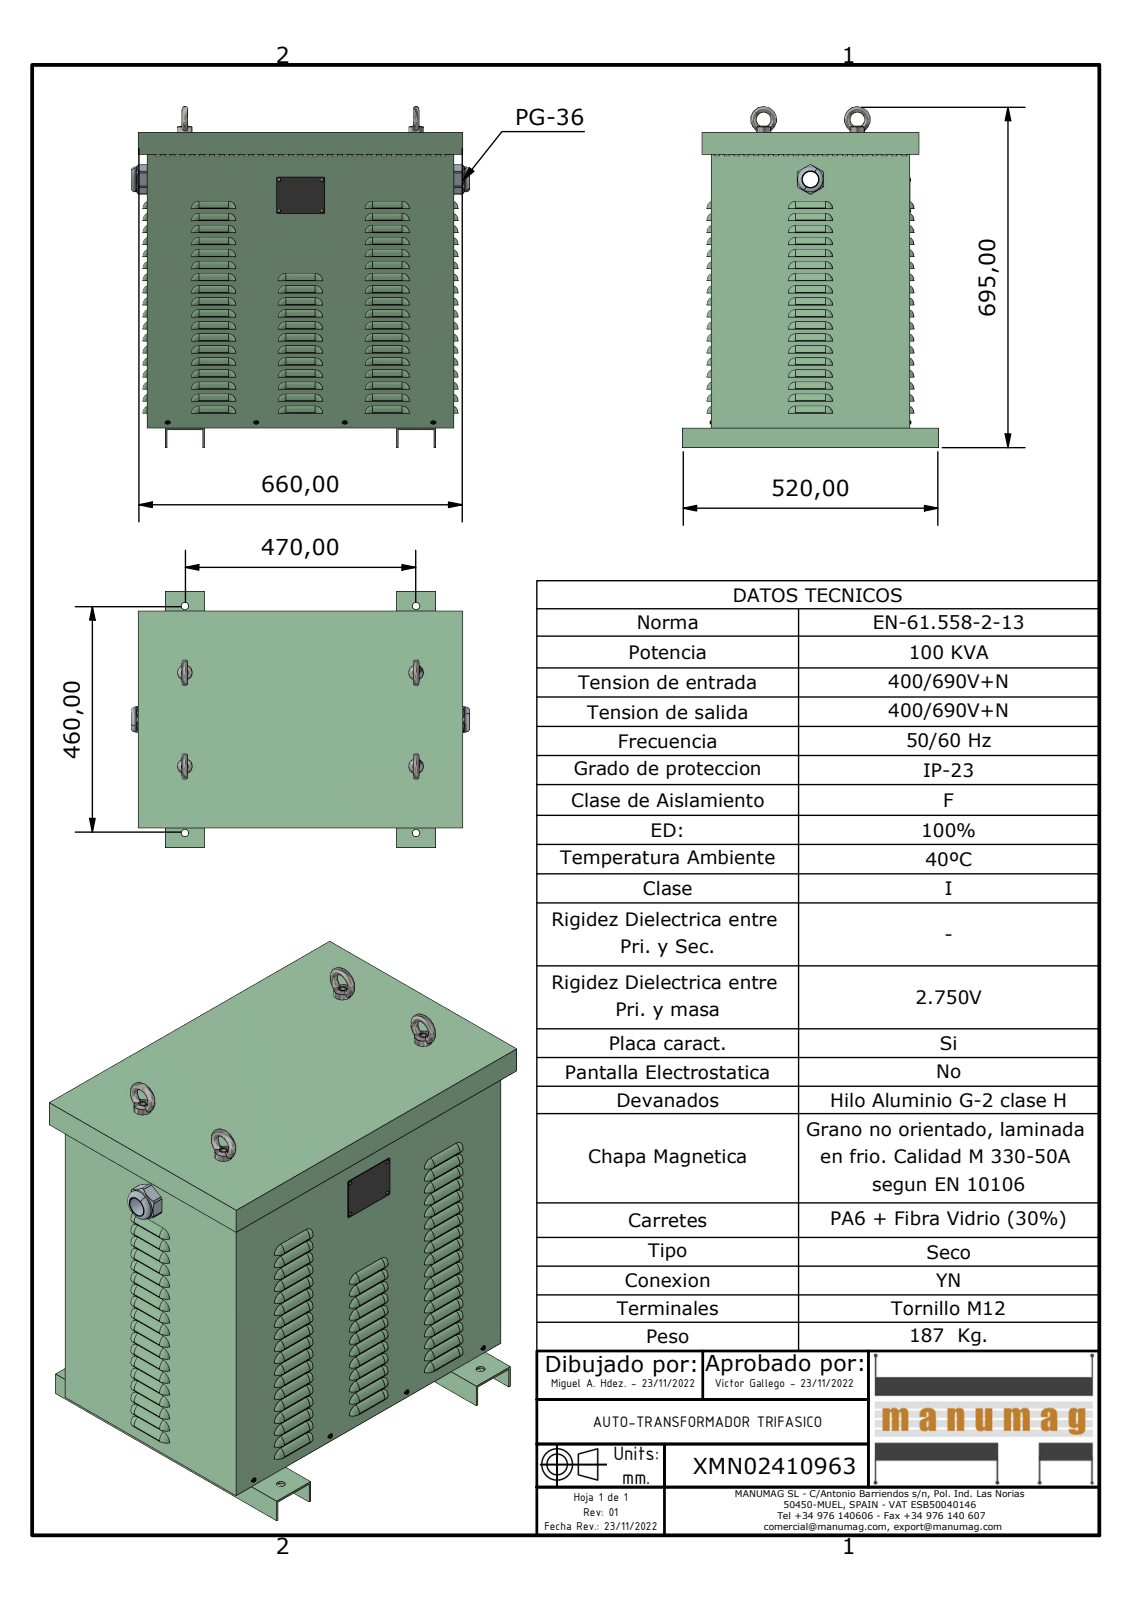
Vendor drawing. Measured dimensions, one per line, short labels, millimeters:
name: XMN02410963; JE100 CUERPO; JE100 BASE; PLACA CARACTERISTICAS (+6 more)
written by: Autodesk Inventor 2023 (AUTOMOTIVE_DESIGN)
unit: mm
bodies: 24 solids, 3065 faces (1141 planar, 1208 cylindrical, 716 other)
size: 695 × 688.2 × 520
volume: 4 880 000 mm³; area: 4 293 000 mm²
holes: 558× ⌀11, 8× ⌀15, 4× ⌀4, 4× ⌀5, 4× ⌀10.11, 1× ⌀32, 1× ⌀48
bosses: 4× ⌀30, 4× ⌀4, 4× ⌀3.62, 4× ⌀3.2, 2× ⌀51.1, 1× ⌀47.45, 1× ⌀47
rounds: 132× R14, 72× R7, 72× R15, 12× R3.88, 8× R2.5, 4× R2, 2× R30
face distances: 2, 400, 600, 621, 398, 402, 602, 619, 598, 623
hole spacings: 30, 15, 582, 582.77, 199, 45, 582.19, 583.74
